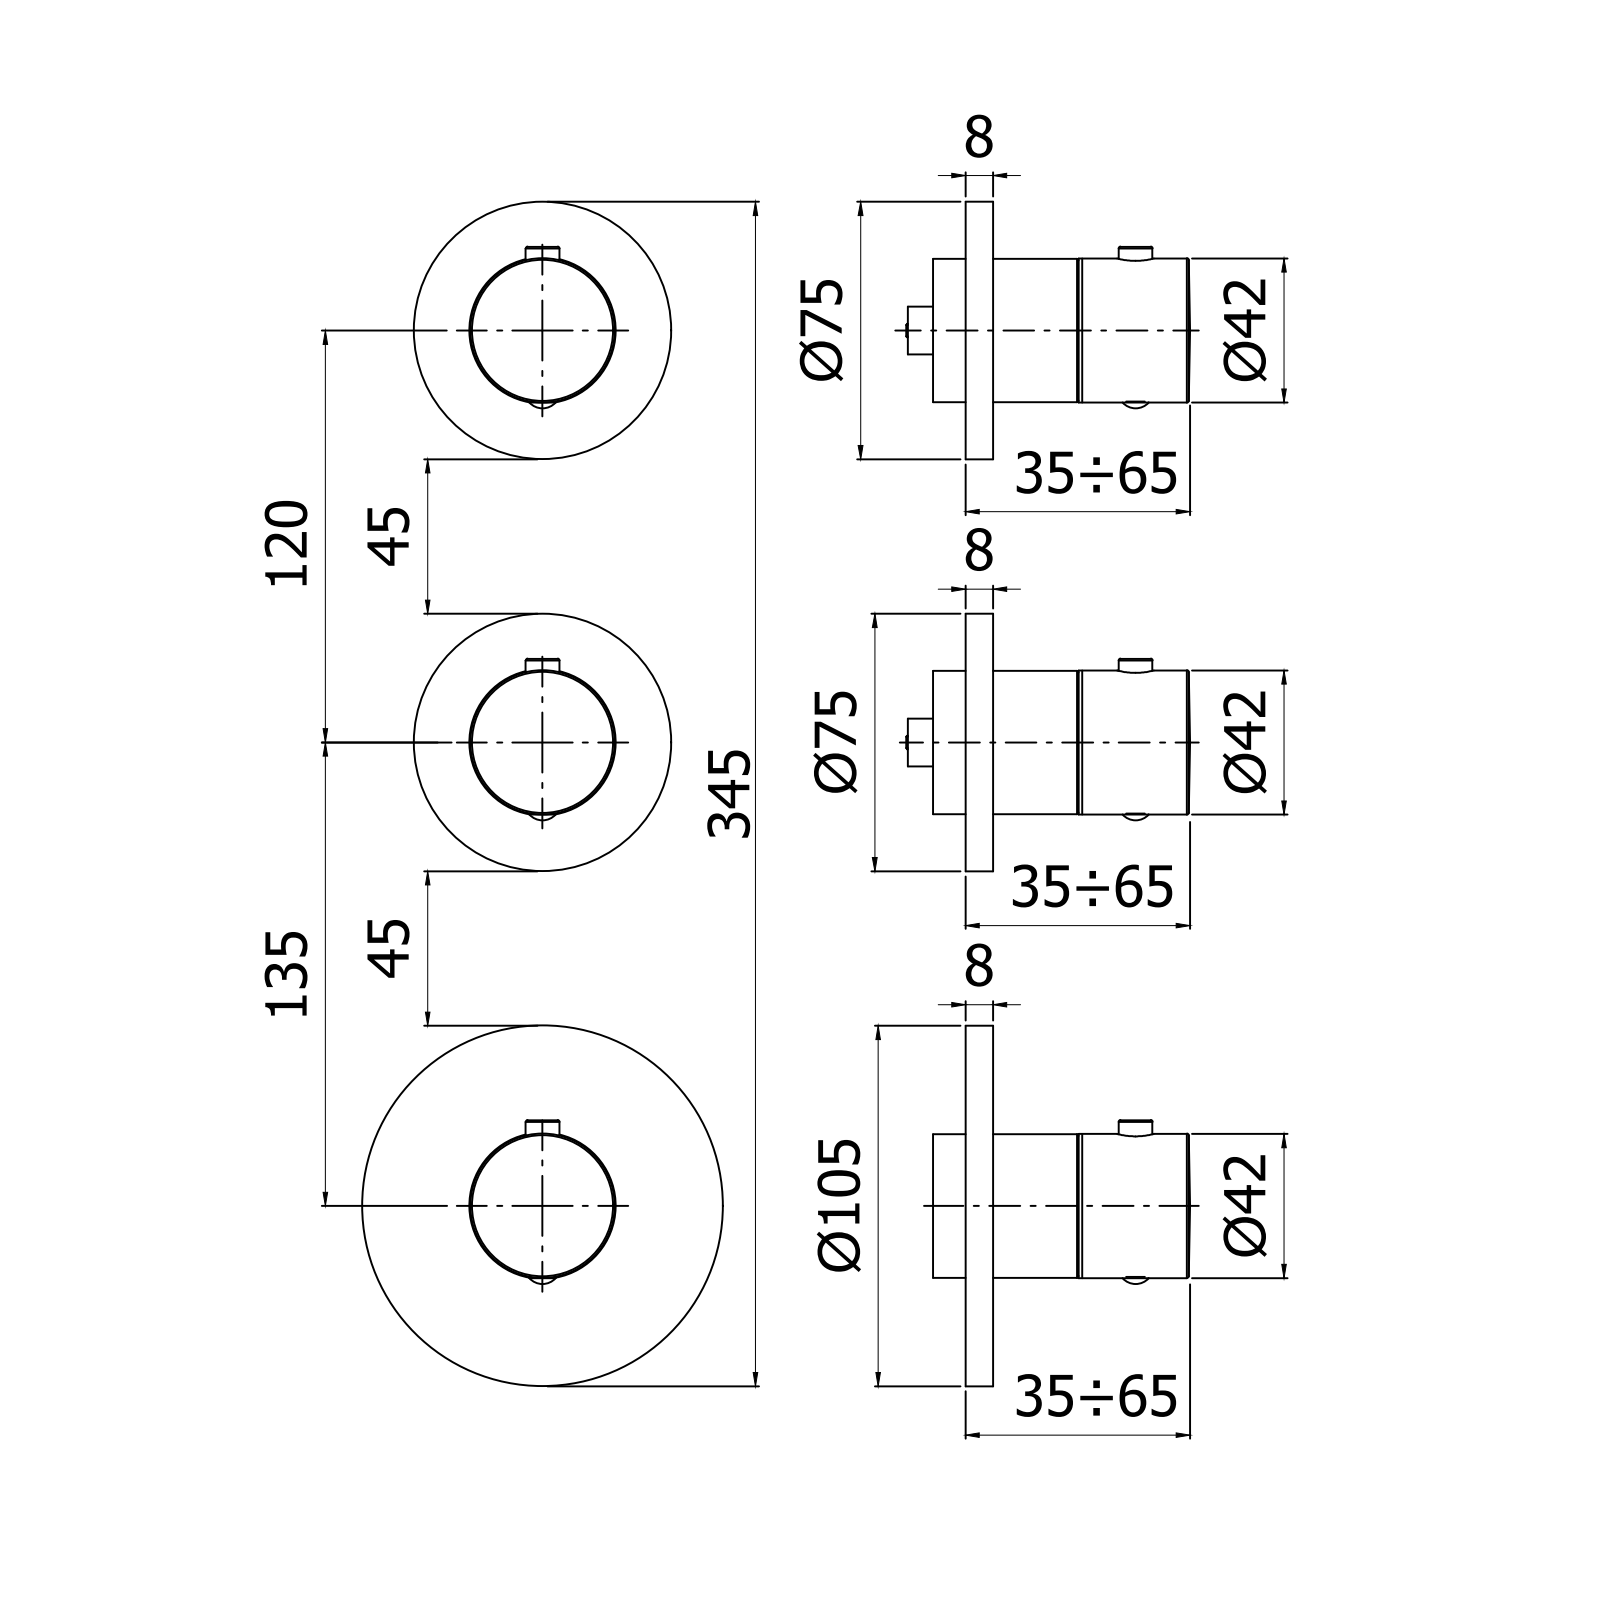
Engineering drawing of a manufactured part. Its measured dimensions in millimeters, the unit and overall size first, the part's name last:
Units: millimetres
Overall size (bounding box): 345 × 105 × 65.37
Round bosses / shafts (diameter × count): ⌀42 ×3, ⌀41.8 ×3, ⌀75 ×2, ⌀105 ×1, ⌀9.8 ×1, ⌀7.6 ×1
Main face-to-face distances: 8, 33, 25, 120, 254.4, 134.4, 45.05, 165.05, 89.35, 300.05
Volume: 377 286 mm³ · Surface area: 64 562 mm²
Bodies: 3 solids, 78 faces (18 planar, 30 cylindrical, 30 other)
Part name (STEP PRODUCT): MDE018CR
STEP written by: CREO PARAMETRIC BY PTC INC, 2020044 (CONFIG_CONTROL_DESIGN)
